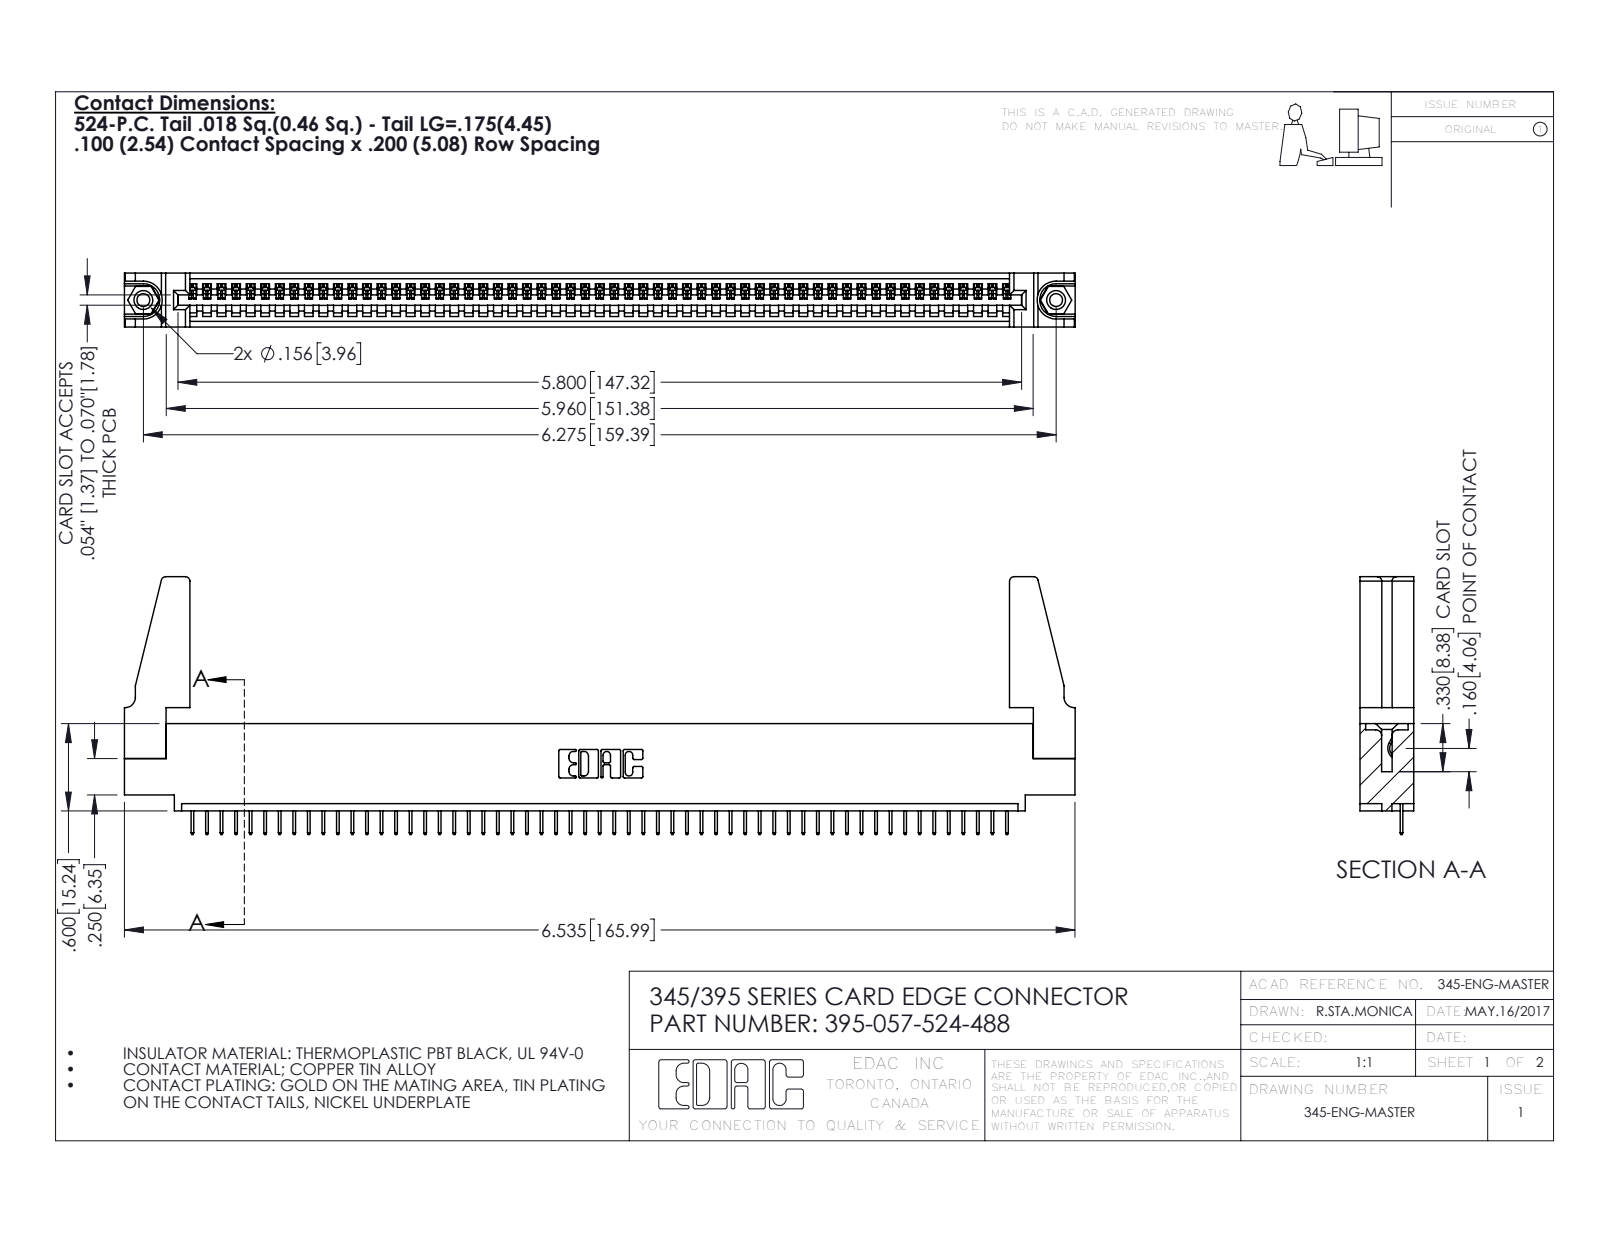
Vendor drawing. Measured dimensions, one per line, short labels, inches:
name: 345-292-001_345-293-124; 345 Part_0.110 Offset - 0.156 Dia-TH; 395-057-524-488; 345-220-078_345-220-088 (+1 more)
written by: SolidWorks 2016 (CONFIG_CONTROL_DESIGN)
unit: in
bodies: 62 solids, 3788 faces (2778 planar, 994 cylindrical, 16 other)
size: 6.536 × 1.772 × 0.37
volume: 1.15 in³; area: 36.3 in²
holes: 2× ⌀0.089, 2× ⌀0.125, 2× ⌀0.156, 1× ⌀0.064
bosses: 2× ⌀0.155
rounds: 114× R0.006, 22× R0.01, 8× R0.03, 6× R0.007, 6× R0.031, 3× R0.026, 2× R0.031, 2× R0.04
face distances: 0.072, 0.298, 0.37, 0.2, 0.098, 0.272, 0.025, 0.225, 0.072, 0.149
hole spacings: 0.27, 6.039, 6.275
